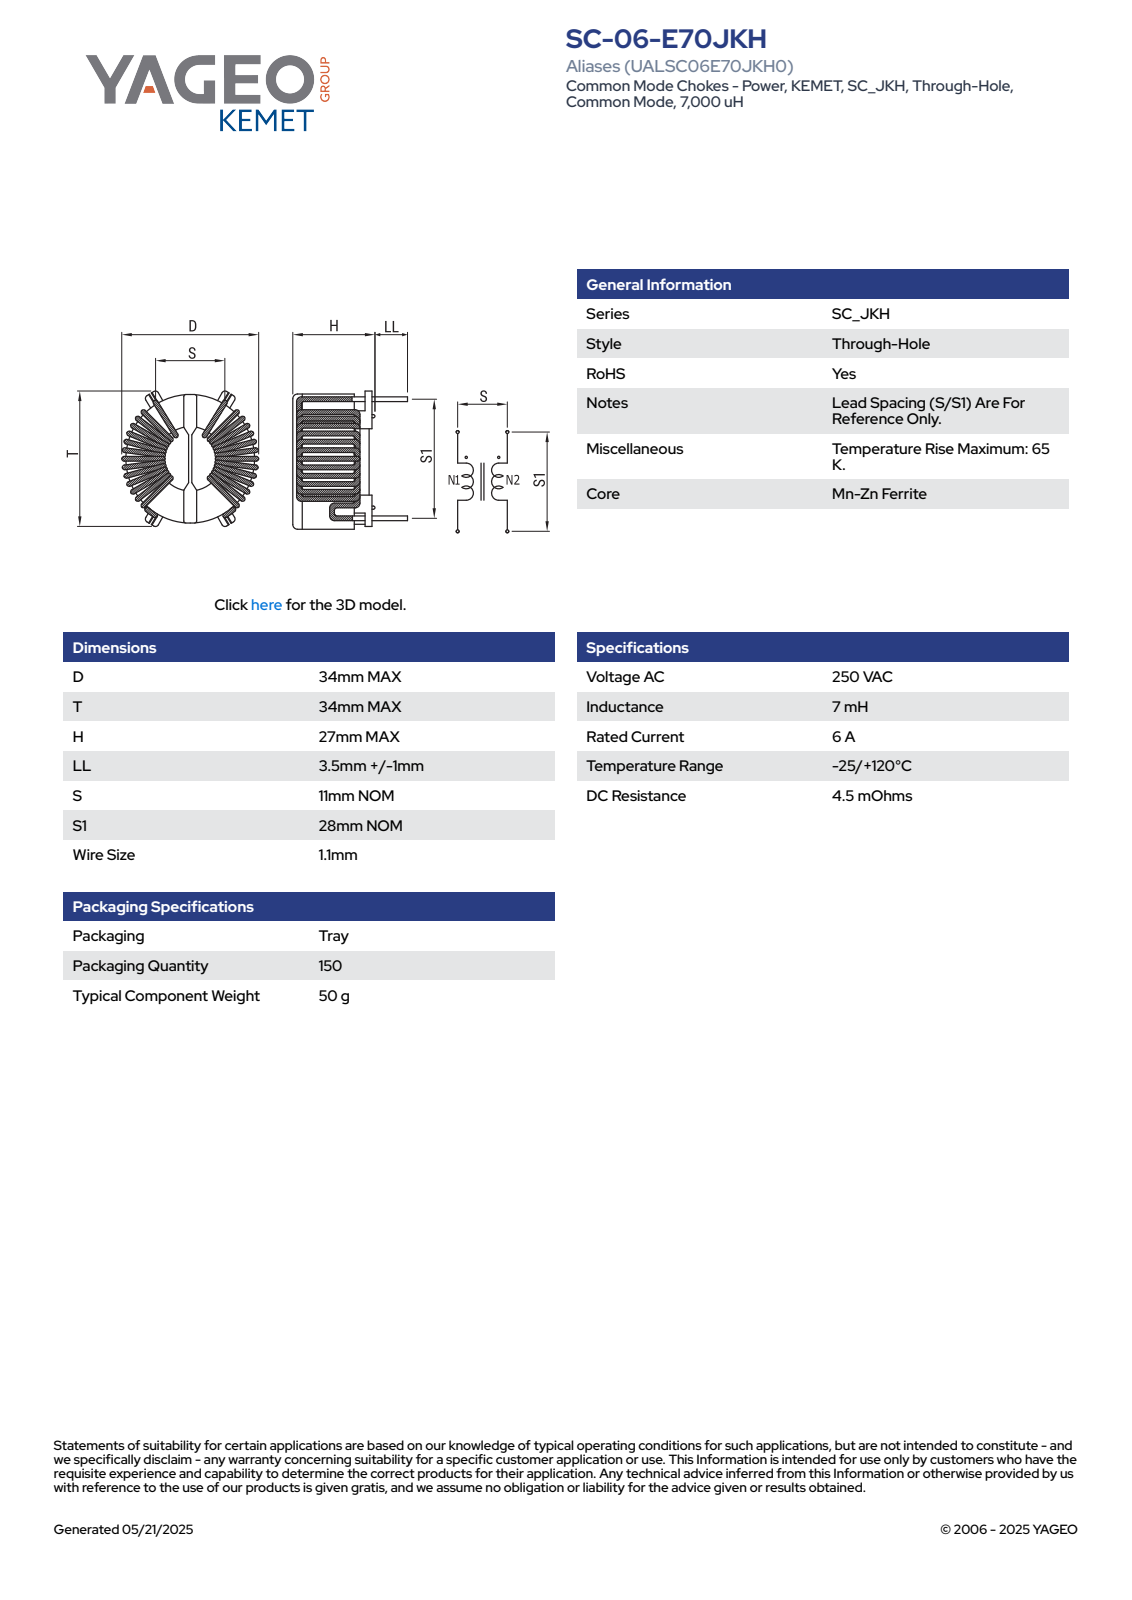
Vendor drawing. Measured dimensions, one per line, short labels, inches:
name: SC-06-E70JKH
written by: SolidWorks 2018 (AUTOMOTIVE_DESIGN)
unit: in
bodies: 4 solids, 443 faces (160 planar, 159 cylindrical, 124 other)
size: 1.339 × 1.339 × 1.201
volume: 1.148 in³; area: 20.21 in²
holes: 1× ⌀0.524, 1× ⌀0.587, 1× ⌀0.591, 1× ⌀0.854, 1× ⌀0.996
bosses: 6× ⌀0.043, 4× ⌀0.039, 1× ⌀1.051, 1× ⌀0.984, 1× ⌀0.72, 1× ⌀0.579
rounds: 40× R0.02, 18× R0.022, 10× R0.008, 1× R0.215, 1× R0.526, 1× R0.533, 1× R0.669
face distances: 0.098, 0.724, 0.482, 0.118, 0.823, 0.669, 0.154, 0.571, 0.031, 0.626
